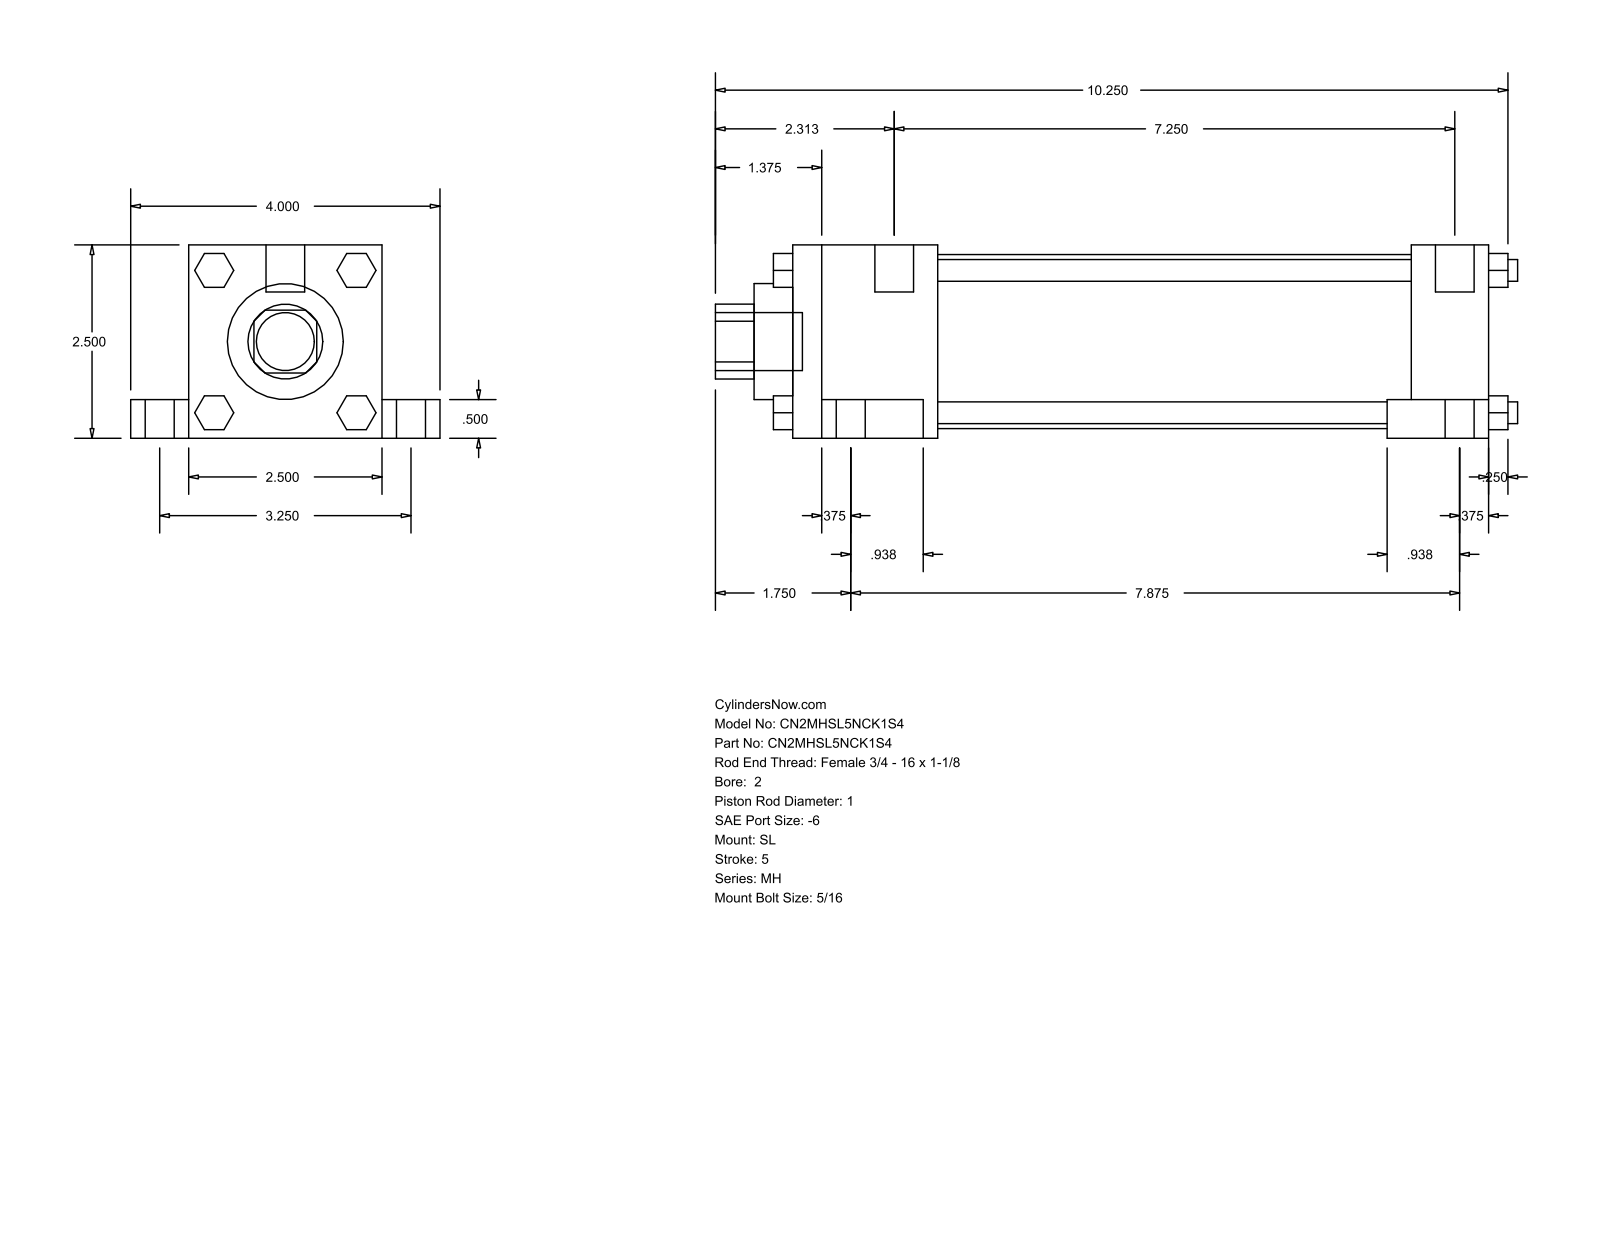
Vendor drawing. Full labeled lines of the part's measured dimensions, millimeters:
Part name (STEP PRODUCT): MH_SL__0200_1
STEP written by: GSSL Pune (CONFIG_CONTROL_DESIGN)
Units: millimetres
Bodies: 0 solids, 148 faces (112 planar, 36 cylindrical, 0 other)
Overall size (bounding box): 263.52 × 101.6 × 63.5
Round holes (diameter × count): ⌀25.4 ×1, ⌀38.1 ×1, ⌀57.15 ×1
Round bosses / shafts (diameter × count): ⌀15.88 ×4, ⌀9.53 ×4, ⌀7.14 ×4, ⌀5.56 ×4, ⌀12.7 ×2, ⌀19.05 ×1
Partial cylindrical surfaces — rounded edges, fillets, slot ends (radius × count): R12.29 ×1
Main face-to-face distances: 63.5, 228.6, 12.7, 19.05, 50.8, 82.55, 9.52, 25.4, 203.2, 47.63
